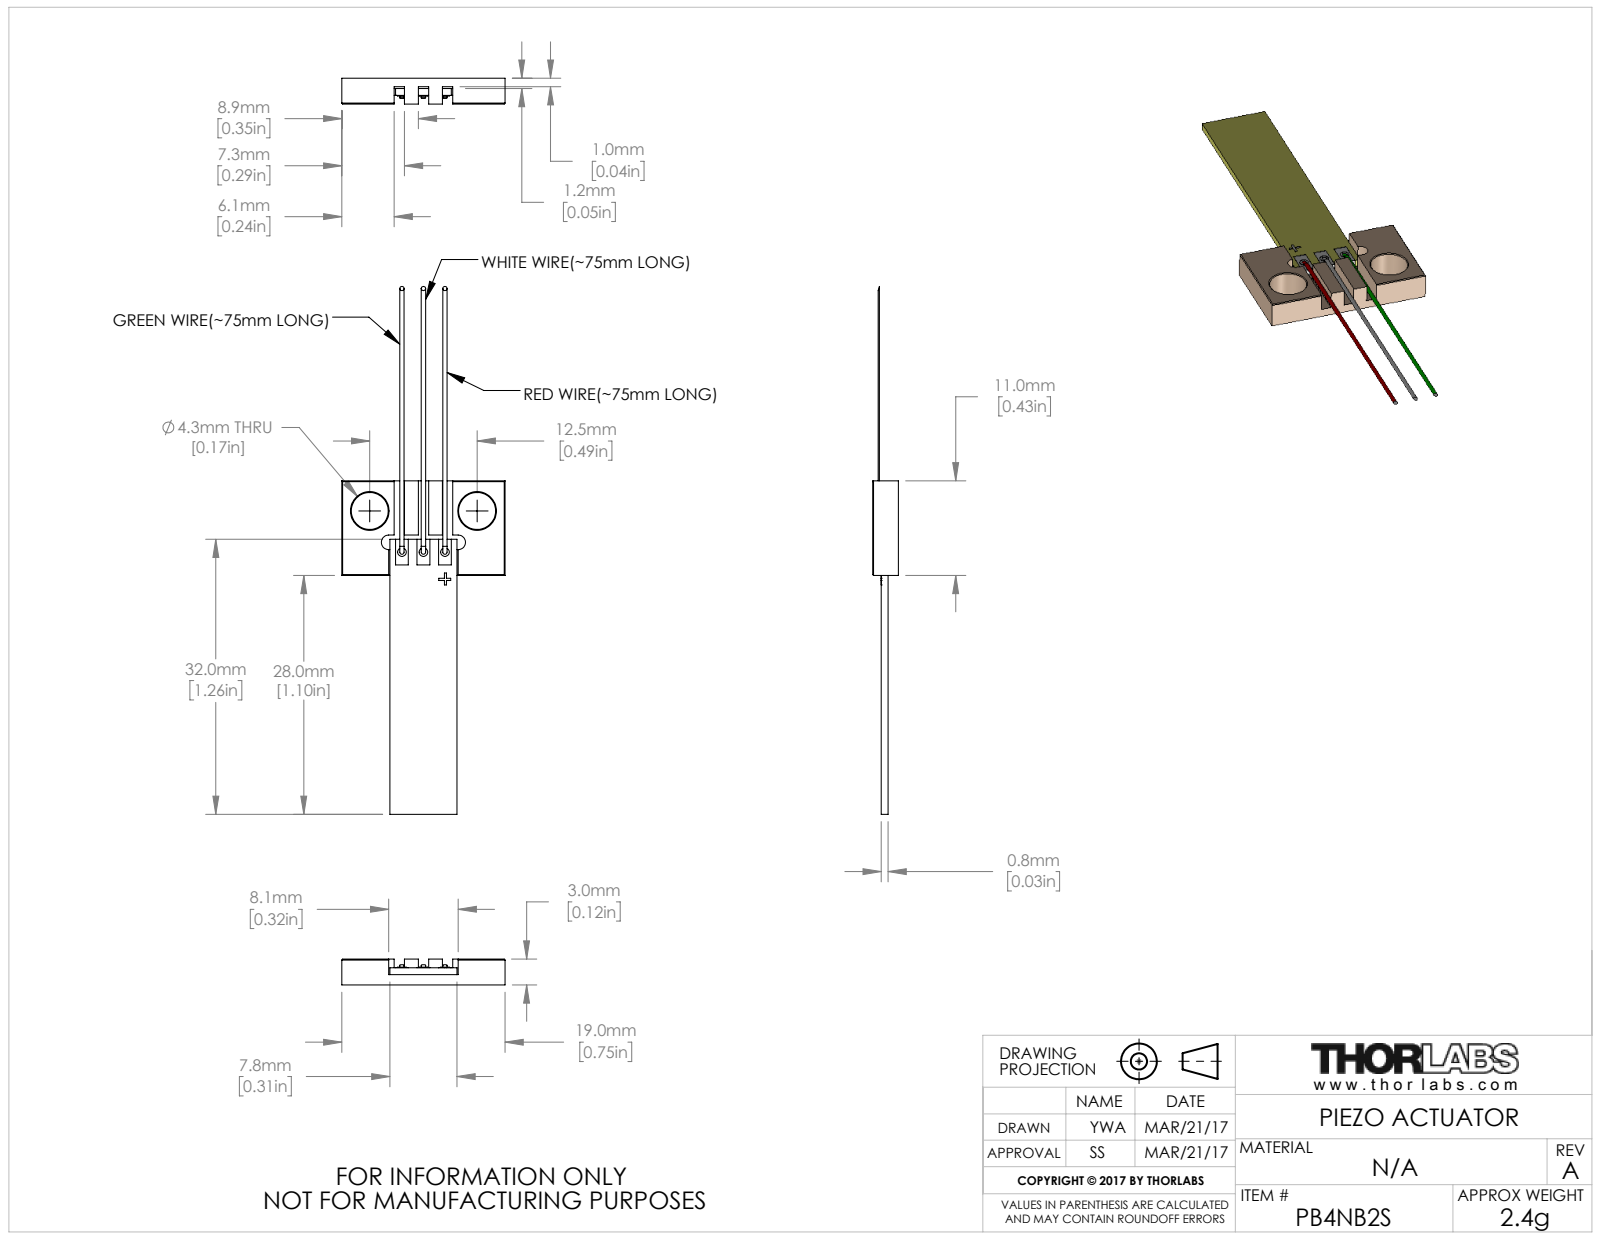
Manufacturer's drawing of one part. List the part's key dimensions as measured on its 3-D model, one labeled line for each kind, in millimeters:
Part name (STEP PRODUCT): CTN010297
STEP written by: SolidWorks 2016 (AUTOMOTIVE_DESIGN)
Units: millimetres
Bodies: 2 solids, 104 faces (75 planar, 13 cylindrical, 16 other)
Overall size (bounding box): 61.4 × 19 × 3
Volume: 620 mm³ · Surface area: 1 368 mm²
Round holes (diameter × count): ⌀4.3 ×2
Round bosses / shafts (diameter × count): ⌀1 ×3
Partial cylindrical surfaces — rounded edges, fillets, slot ends (radius × count): R0.8 ×2
Main face-to-face distances: 0.8, 1.2, 2, 1, 3, 1.8, 5.6, 13.4, 7.3, 6.1
Hole centre spacings: 12.5
